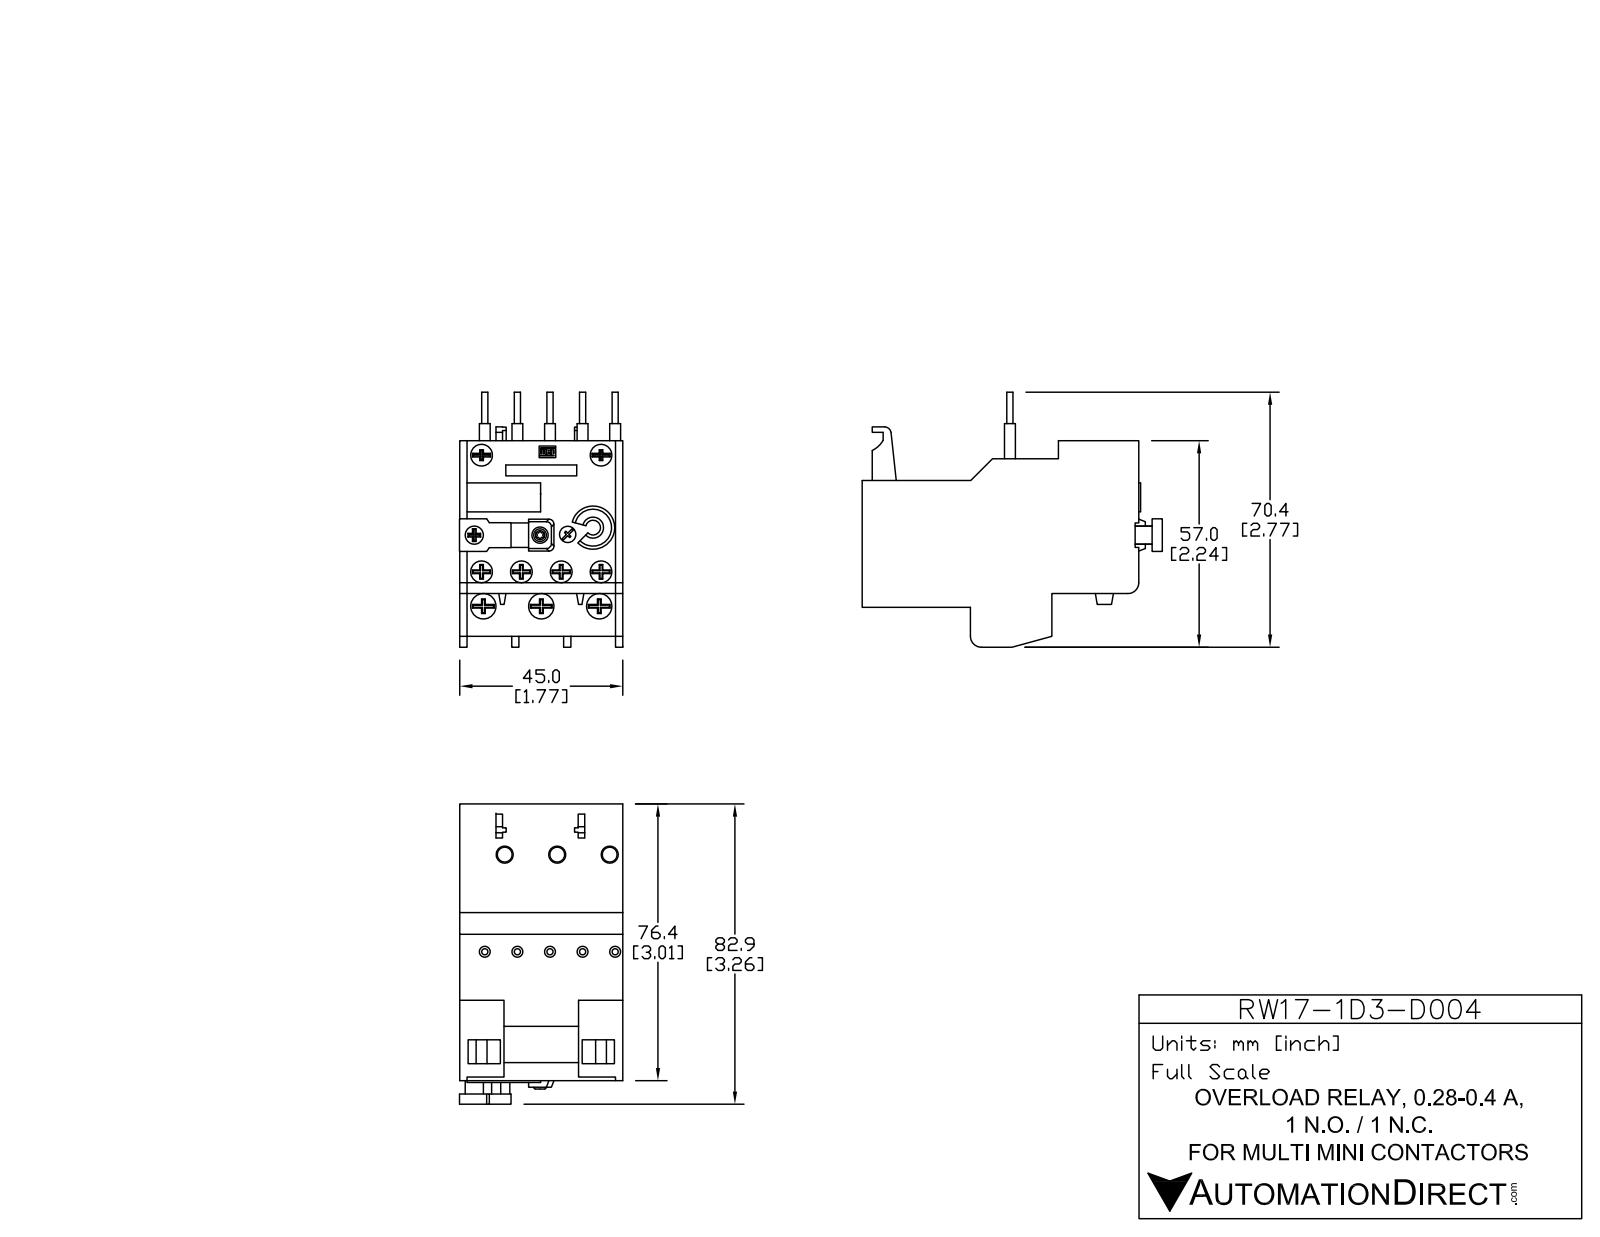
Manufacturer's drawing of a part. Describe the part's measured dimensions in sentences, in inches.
The part is named "RW17D-1D3-D004". Its 3-D file was written by "SolidWorks 2013 (AUTOMOTIVE_DESIGN)". It is 18 solids with 756 faces: 515 planar, 214 cylindrical and 27 other. Overall it measures 3.254 by 2.776 by 1.793 inches. Its volume is 7.778 cubic inches and its surface area 53.79 square inches. Round holes: 6 of diameter 0.236, 3 of diameter 0.157, 3 of diameter 0.276, 3 of diameter 0.295, 1 of diameter 0.177, 1 of diameter 0.187, 1 of diameter 0.21, 1 of diameter 0.217, 1 of diameter 0.41. Round bosses or shafts: 7 of diameter 0.217, 7 of diameter 0.118, 5 of diameter 0.069, 2 of diameter 0.22, 2 of diameter 0.128, 1 of diameter 0.253, 1 of diameter 0.242, 1 of diameter 0.187. Partial cylindrical surfaces (rounded edges, fillets, slot ends): 20 of radius 0.02, 12 of radius 0.01, 9 of radius 0.039, 6 of radius 0.178, 4 of radius 0.231, 4 of radius 0.309, 3 of radius 0.059, 2 of radius 0.049. The main face-to-face distances are 1.791, 0.059, 0.427, 0.433, 3.008, 1.378, 0.056, 2.952, 2.949, 0.236. The hole center spacings are 0.591, 0.337, 0.423, 1.181, 0.416, 0.467, 0.561, 0.841.
